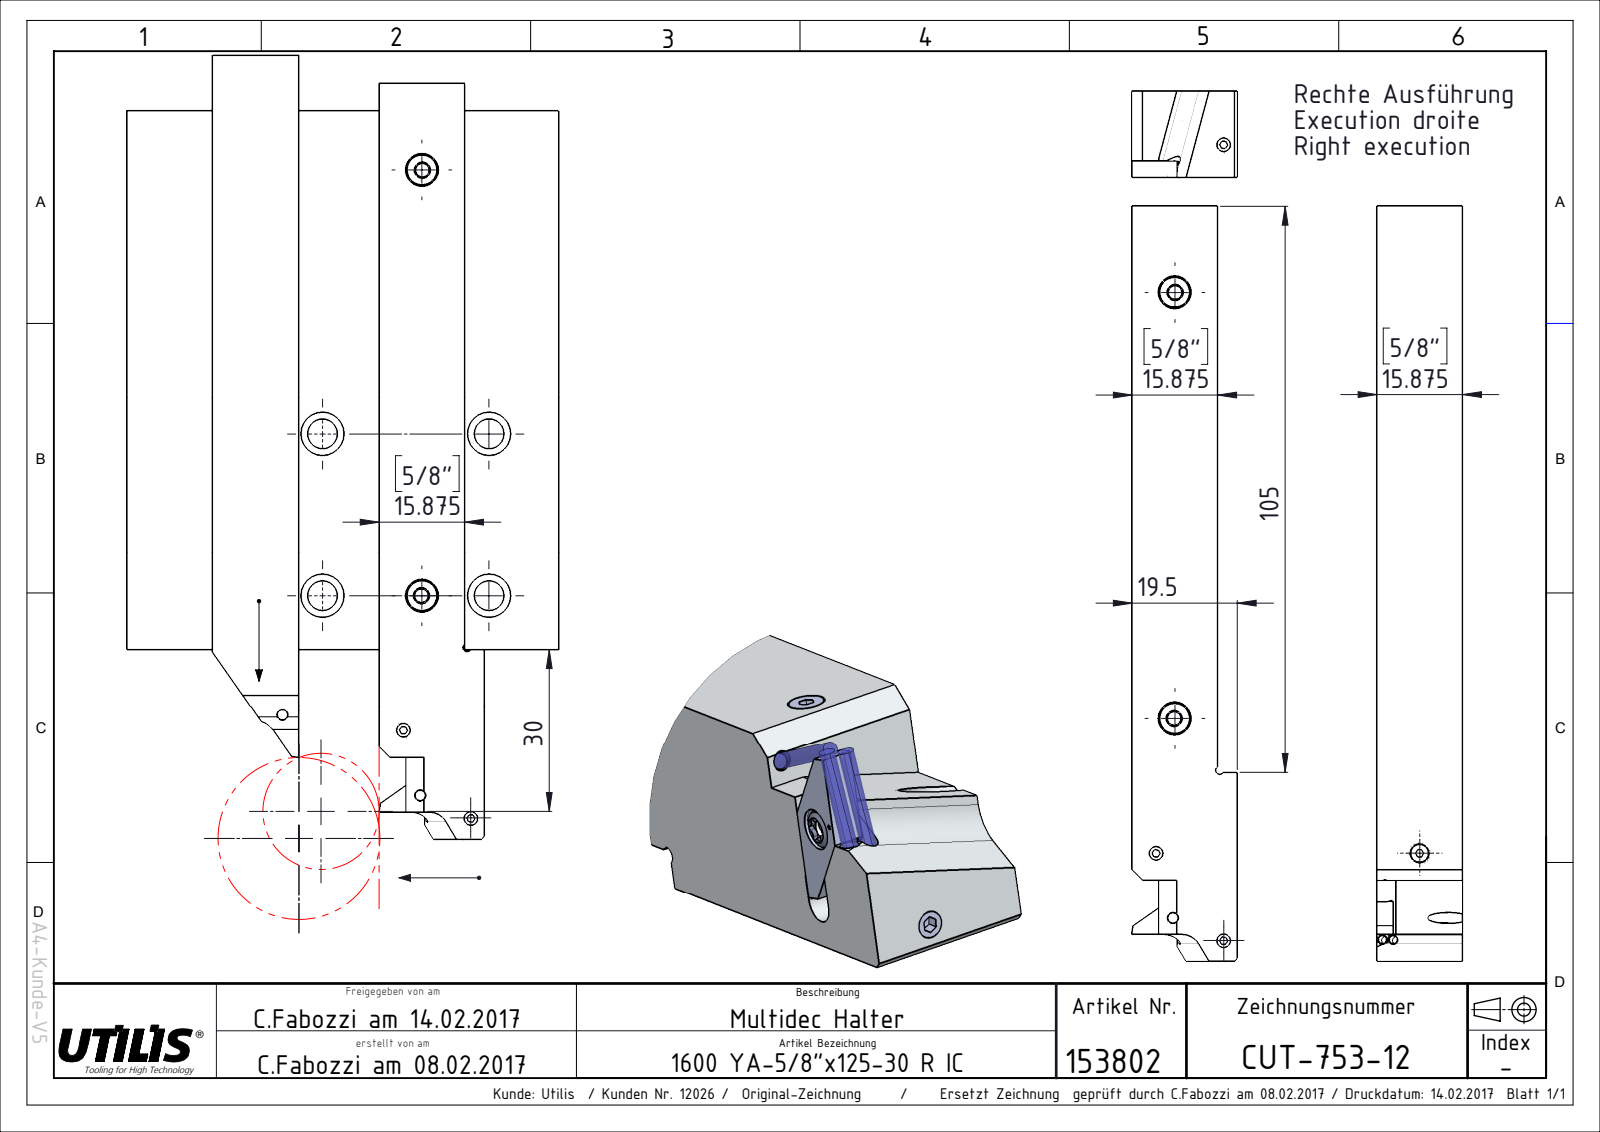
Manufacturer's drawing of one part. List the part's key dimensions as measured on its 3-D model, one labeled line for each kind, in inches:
Part name (STEP PRODUCT): CUT-753_Kunde_12; CUT-753-12; CUT-753_Platte_10006
STEP written by: SolidWorks 2016 (CONFIG_CONTROL_DESIGN)
Units: inches
Bodies: 2 solids, 69 faces (44 planar, 11 cylindrical, 14 other)
Overall size (bounding box): 5.512 × 0.768 × 0.625
Volume: 2.16 in³ · Surface area: 15.12 in²
Round holes (diameter × count): ⌀0.071 ×1, ⌀0.114 ×1, ⌀0.122 ×1
Partial cylindrical surfaces — rounded edges, fillets, slot ends (radius × count): R0.02 ×1, R0.03 ×1, R0.061 ×1, R0.067 ×1, R0.138 ×1
Main face-to-face distances: 0.625, 0.625, 0.768, 0.143, 5.512, 0.118, 0.507, 0.591, 4.921, 0.236
